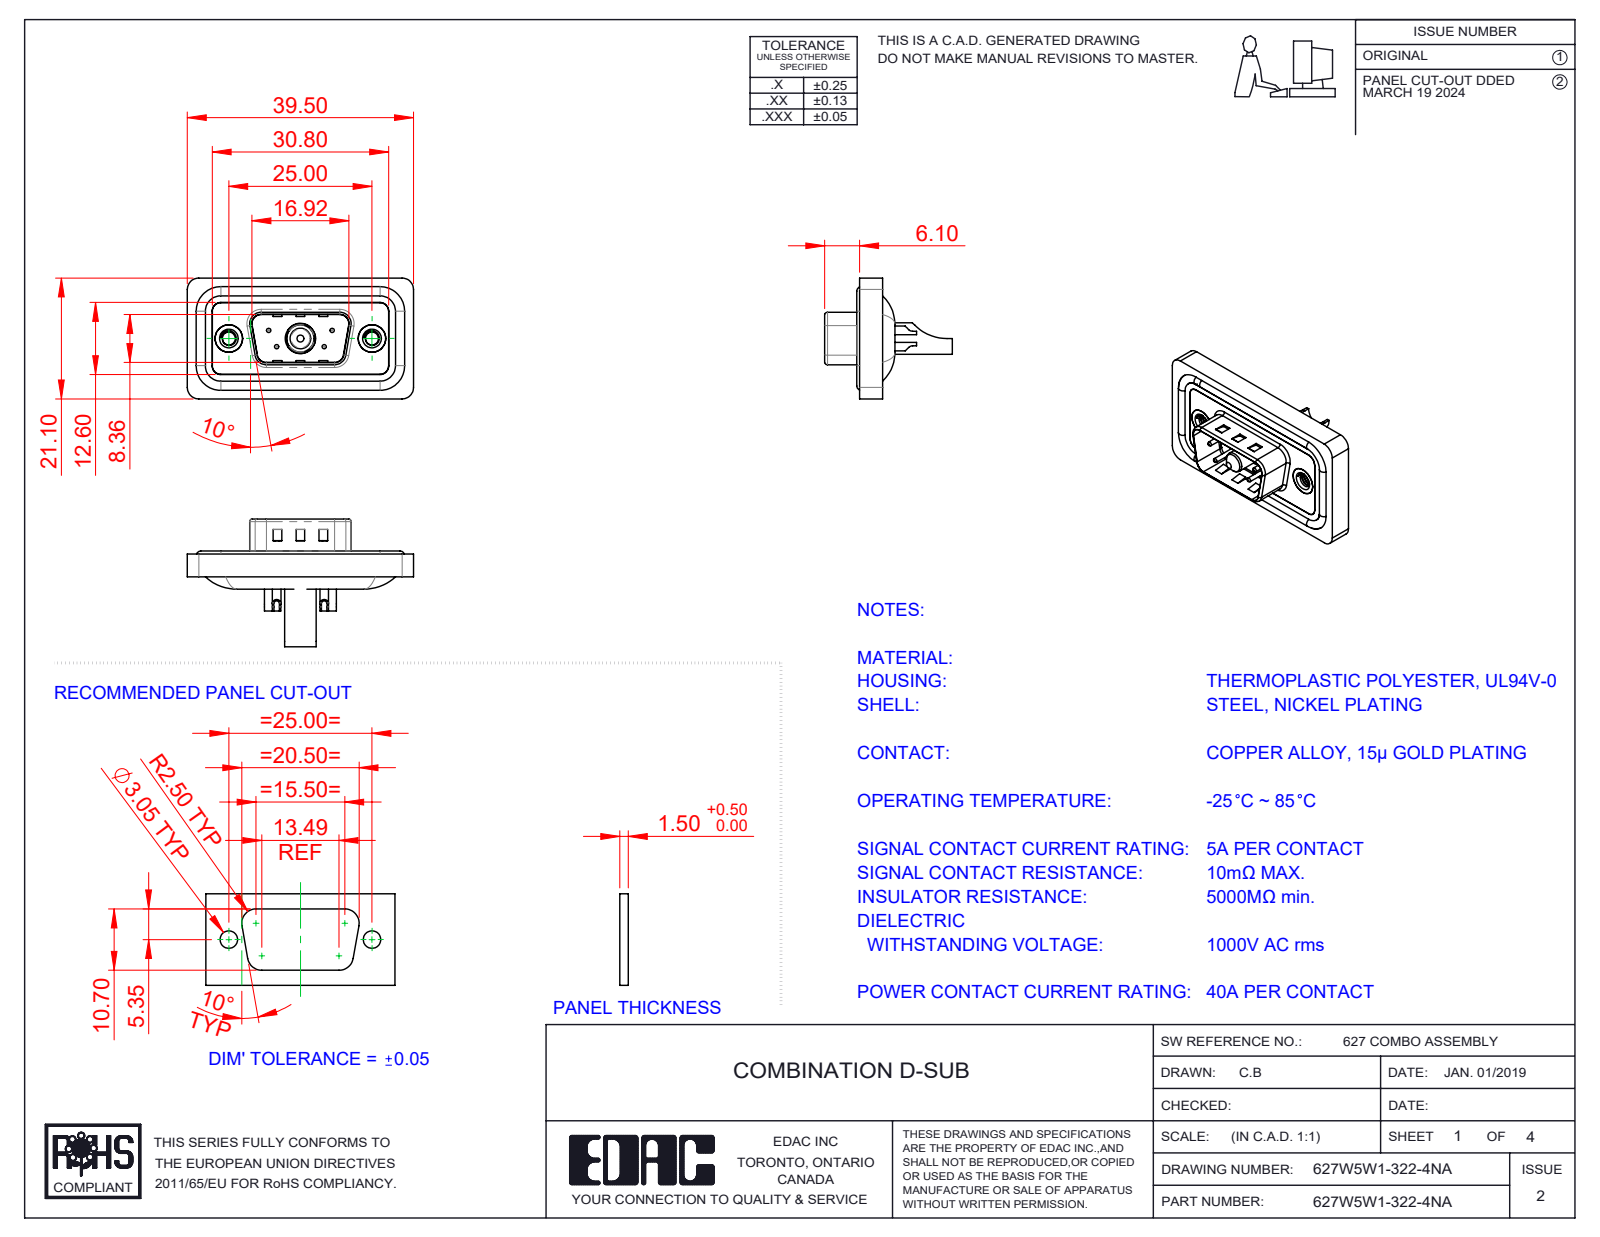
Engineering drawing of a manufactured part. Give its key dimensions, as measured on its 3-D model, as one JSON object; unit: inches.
{"part_name": "627Combo Shell Front_09 Contacts; Power Pin_40A SC; 627Combo Shell Rear_09 Contacts; 627Combo Contact Row 2_22 (+5 more)", "step_written_by": "SolidWorks 2023 (CONFIG_CONTROL_DESIGN)", "units": "inches", "bodies": {"solids": 13, "faces": 600, "planar": 193, "cylindrical": 266, "other": 141}, "overall_size": [1.555, 0.878, 0.831], "volume_in3": 0.271, "surface_area_in2": 11.02, "round_holes": [[0.03, 4], [0.039, 4], [0.063, 4], [0.079, 4], [0.089, 2], [0.157, 2], [0.189, 2], [0.197, 2], [0.181, 1], [0.191, 1], [0.209, 1]], "round_bosses_or_shafts": [[0.063, 4], [0.059, 4], [0.193, 2], [0.217, 1], [0.205, 1], [0.187, 1], [0.148, 1], [0.142, 1]], "partial_cylinders_radius": [[0.059, 22], [0.079, 18], [0.02, 8], [0.063, 8], [0.039, 6], [0.01, 4], [0.024, 4], [0.026, 4]], "face_to_face_distances": [0.016, 0.043, 0.114, 0.063, 0.122, 0.02, 0.059, 0.098, 0.157, 0.031], "hole_center_spacings": [0.124, 0.225, 0.28, 0.492, 0.713, 0.173, 0.173, 0.327]}
